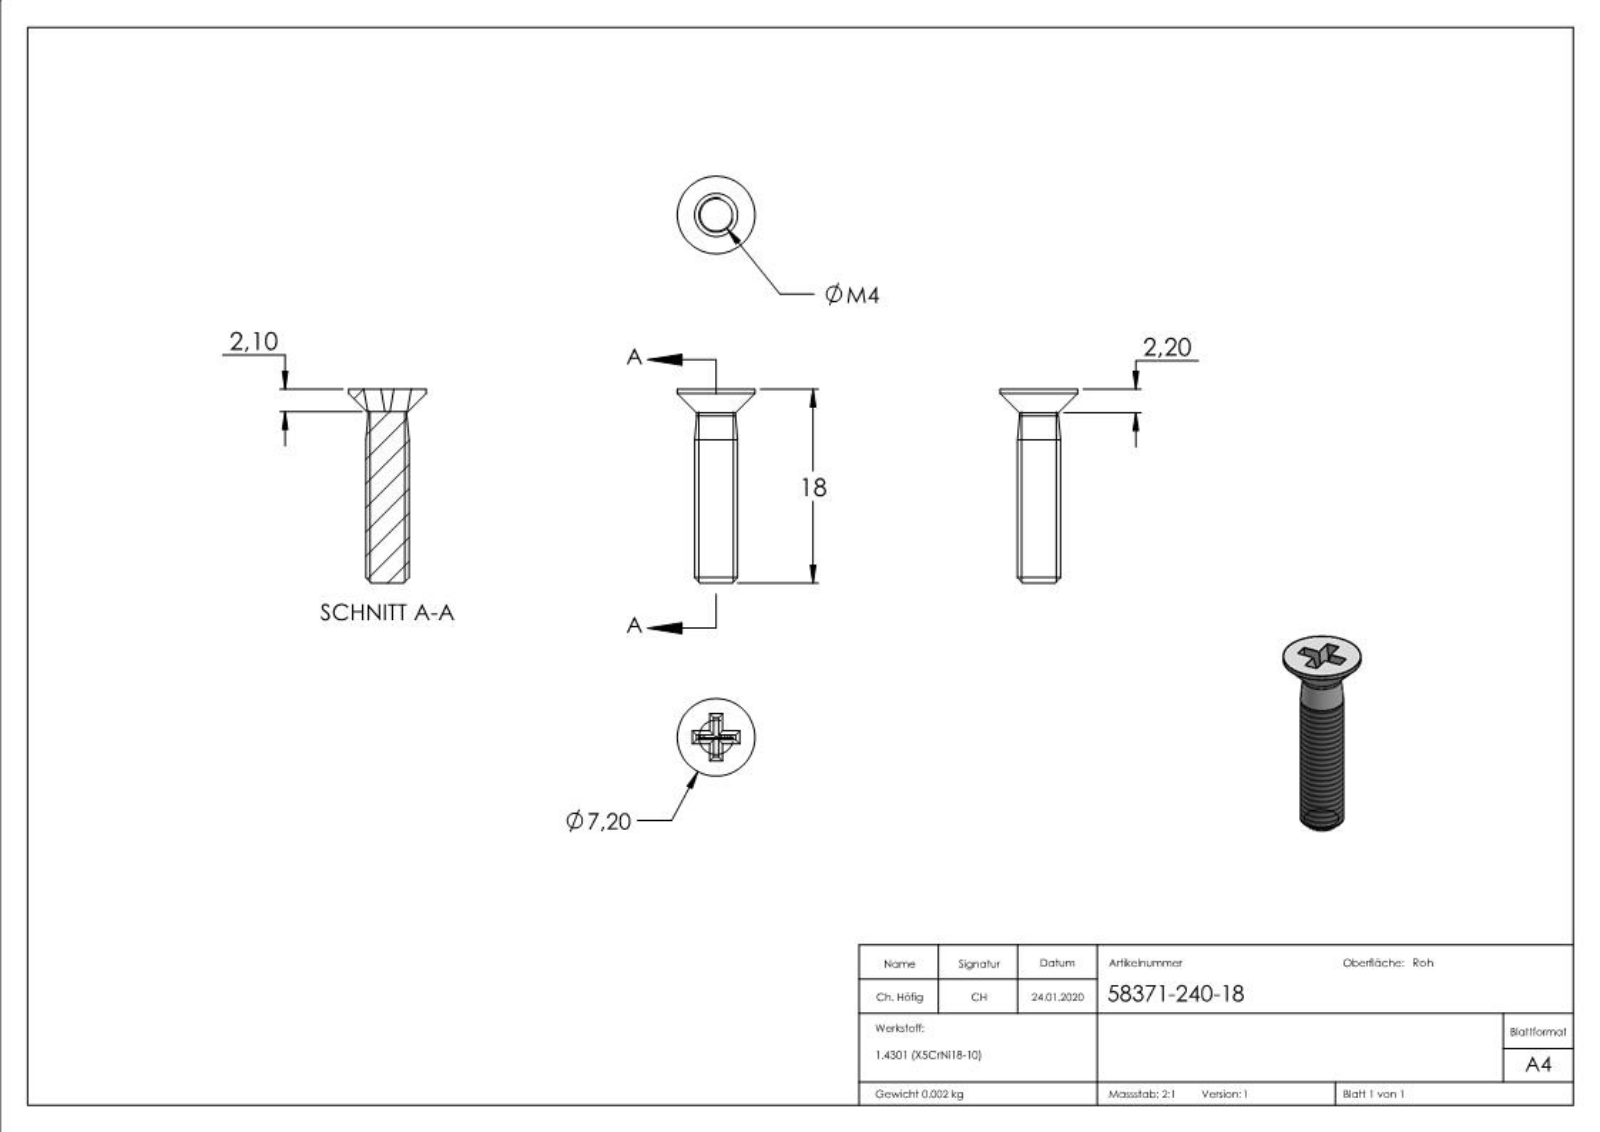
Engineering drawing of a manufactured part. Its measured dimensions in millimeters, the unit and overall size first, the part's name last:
Units: millimetres
Overall size (bounding box): 18 × 7.2 × 7.2
Round bosses / shafts (diameter × count): ⌀7.2 ×1, ⌀4 ×1, ⌀3.6 ×1
Main face-to-face distances: 1.58, 18, 2.1, 15.9, 15.8, 2.2, 0.44, 1.77, 2.57, 0.8
Volume: 240 mm³ · Surface area: 328 mm²
Bodies: 1 solid, 277 faces (152 planar, 3 cylindrical, 122 other)
Part name (STEP PRODUCT): 58371-240-18
STEP written by: SolidWorks 2015 (CONFIG_CONTROL_DESIGN)
